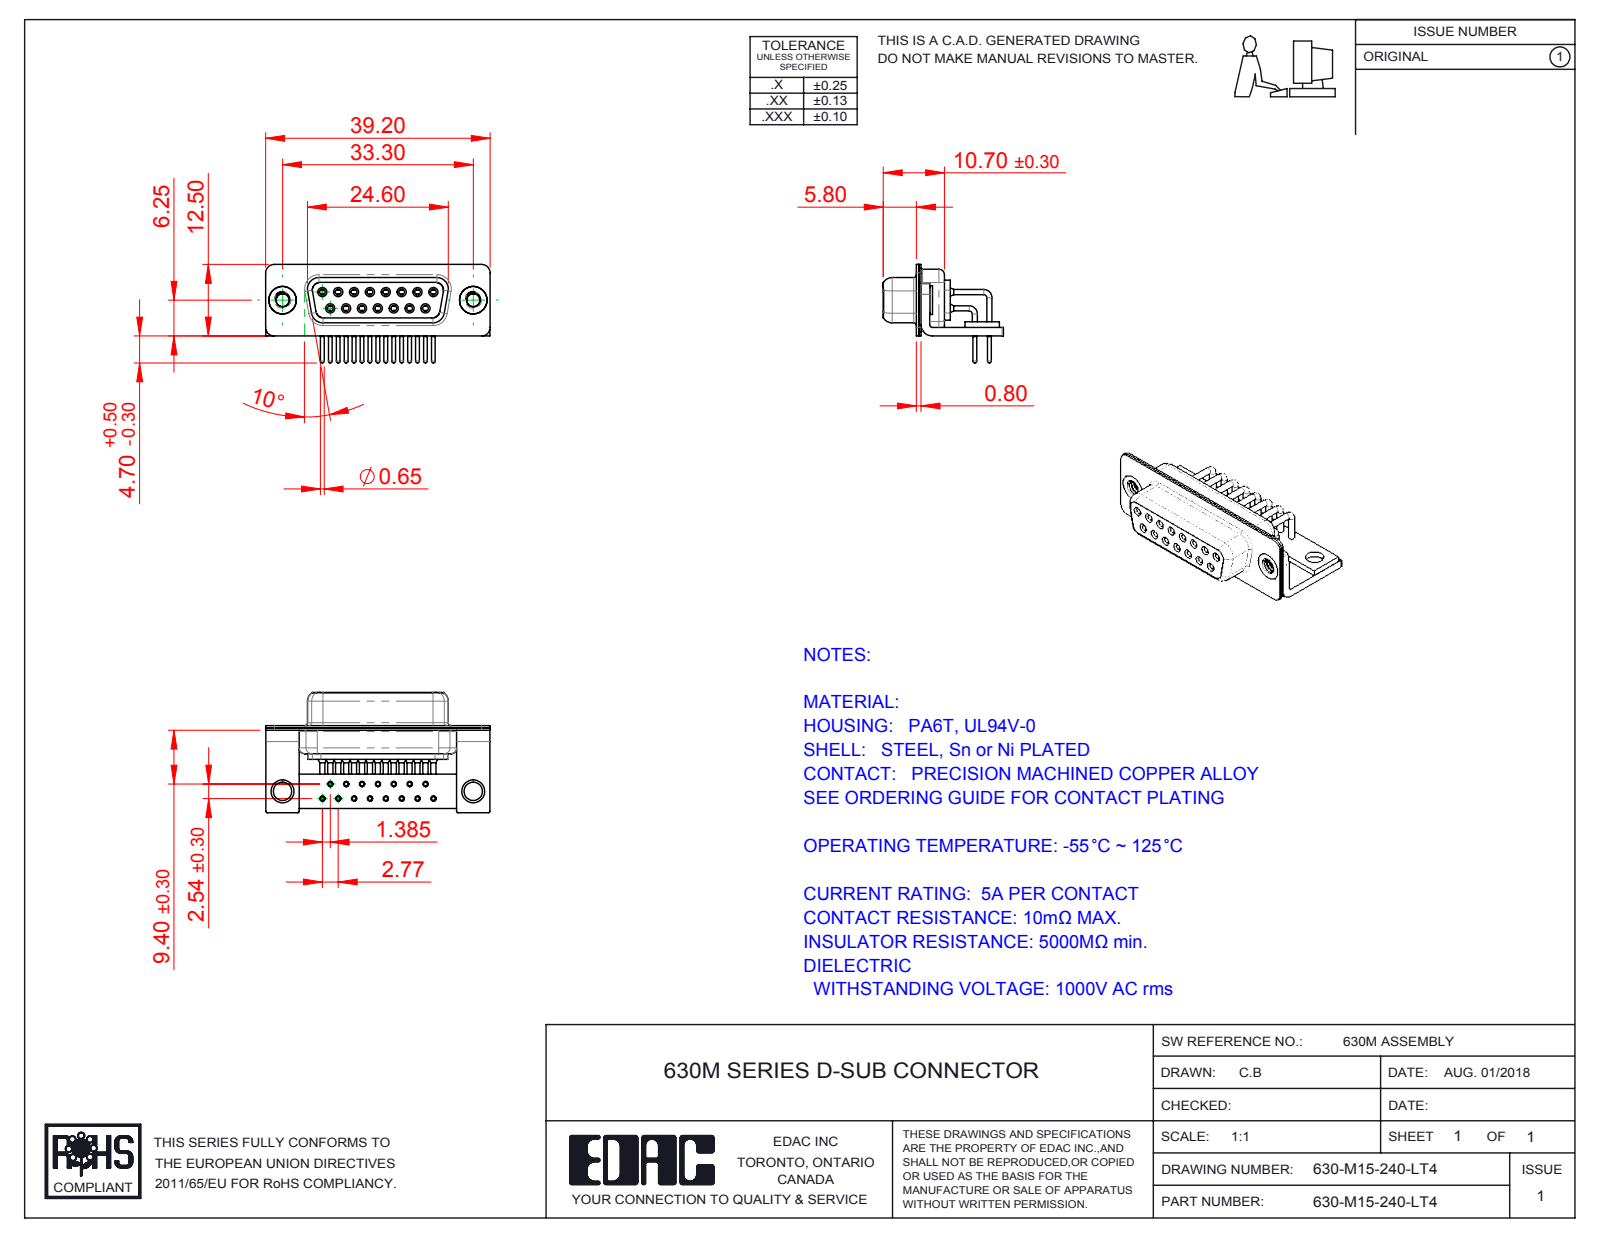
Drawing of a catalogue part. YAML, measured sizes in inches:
part_name: "630-M15-240-LT4; 630M Housing_15 Contacts; 630M Shell Front_15 Contacts; 630M Shell Rear_15 Contacts (+5 more)"
step_written_by: "SolidWorks 2016 (CONFIG_CONTROL_DESIGN)"
units: inches
bodies: {solids: 23, faces: 1154, planar: 318, cylindrical: 534, other: 302}
overall_size: [1.543, 0.827, 0.677]
volume: 0.186
surface_area: 11.96
round_holes:
  - {diameter: 0.035, count: 15}
  - {diameter: 0.039, count: 15}
  - {diameter: 0.043, count: 15}
  - {diameter: 0.067, count: 15}
  - {diameter: 0.071, count: 15}
  - {diameter: 0.079, count: 15}
  - {diameter: 0.089, count: 2}
  - {diameter: 0.126, count: 2}
  - {diameter: 0.157, count: 2}
  - {diameter: 0.189, count: 2}
round_bosses_or_shafts:
  - {diameter: 0.035, count: 27}
  - {diameter: 0.063, count: 15}
  - {diameter: 0.059, count: 15}
  - {diameter: 0.026, count: 15}
  - {diameter: 0.197, count: 2}
  - {diameter: 0.193, count: 2}
partial_cylinders:
  - {radius: 0.01, count: 16}
  - {radius: 0.059, count: 16}
  - {radius: 0.079, count: 13}
  - {radius: 0.053, count: 8}
  - {radius: 0.063, count: 8}
  - {radius: 0.02, count: 5}
  - {radius: 0.024, count: 4}
  - {radius: 0.026, count: 4}
face_to_face_distances: [0.016, 0.031, 0.091, 0.368, 0.075, 0.059, 0.039, 0.057, 0.352, 0.033]
hole_center_spacings: [0.109, 0.218, 0.327, 0.124, 0.192, 0.436, 0.114, 0.29]
